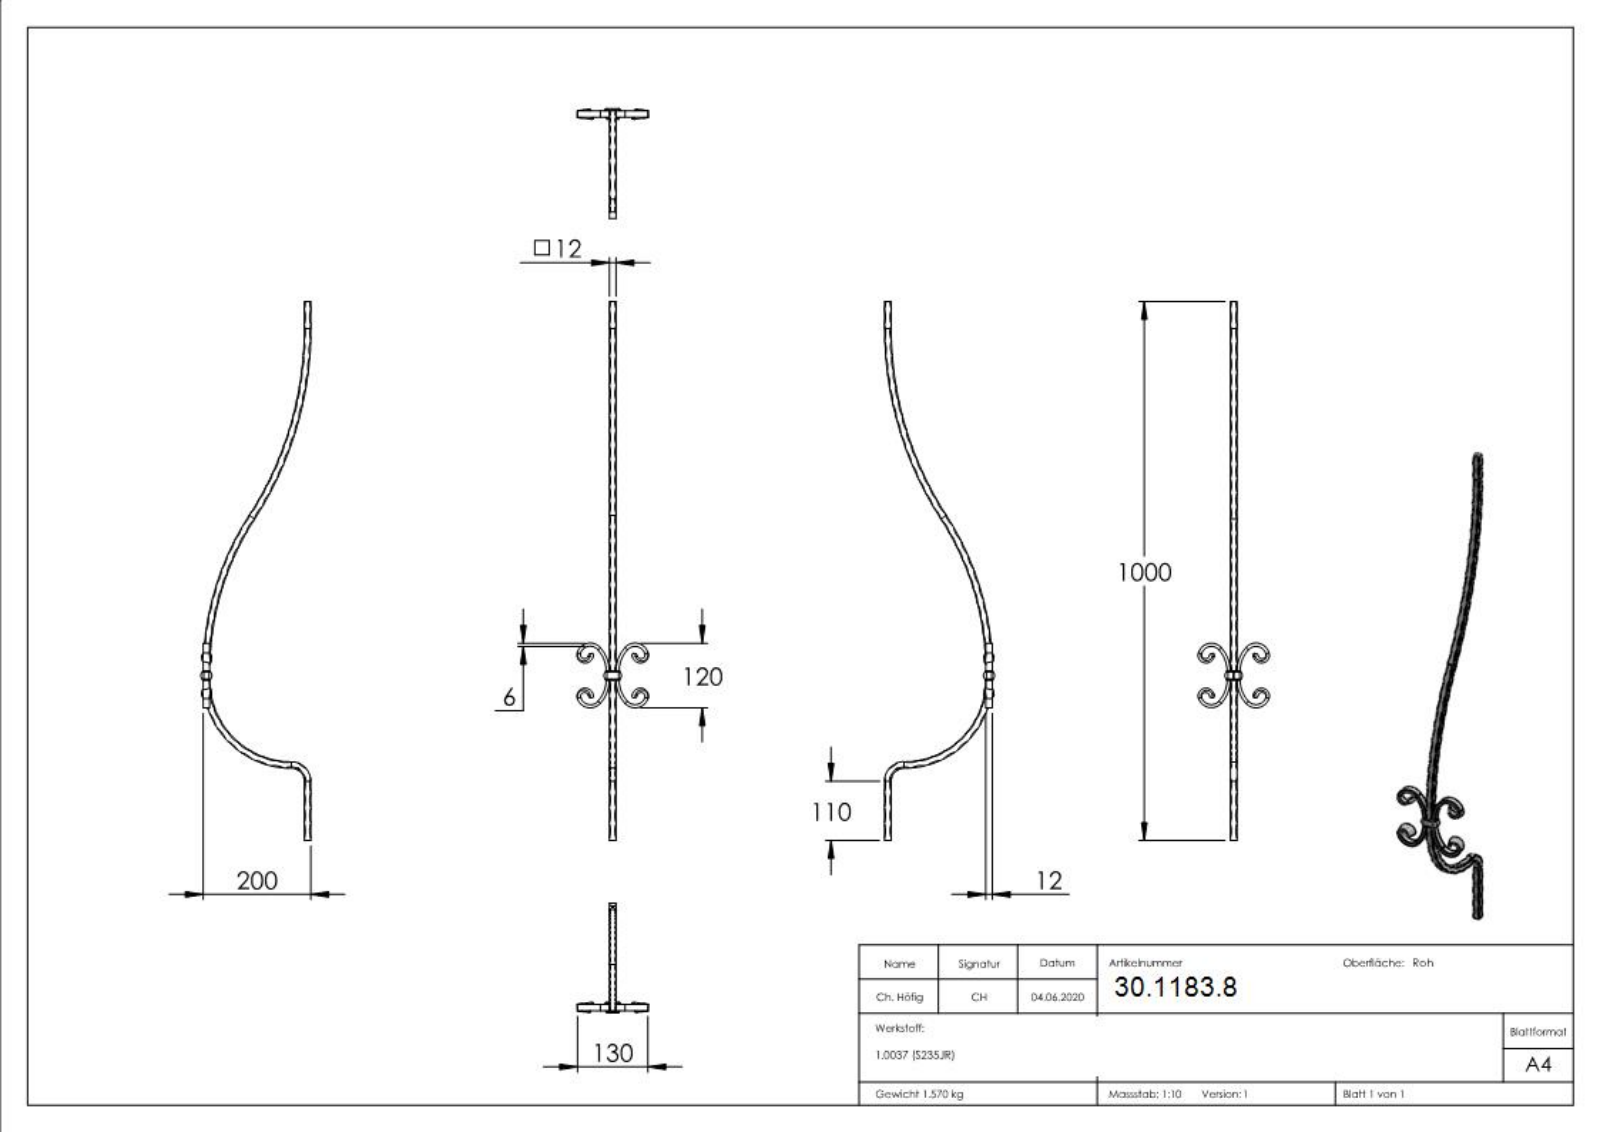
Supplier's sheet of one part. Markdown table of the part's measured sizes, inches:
| quantity | value |
| --- | --- |
| part name | 1712; 1712 Teil2; 1712 Teil2_1712 Teil2; 1712 Teil1 (+2 more) |
| STEP written by | SolidWorks 2015 (CONFIG_CONTROL_DESIGN) |
| units | inches |
| bodies | 4 solids, 453 faces (156 planar, 43 cylindrical, 254 other) |
| overall size | 39.37 × 8.031 × 5.221 |
| volume | 12.31 in³ |
| surface area | 119.9 in² |
| partial cylindrical surfaces (radius × count) | 0.031 × 8, 0.039 × 4, 0.33 × 4, 0.748 × 4, 0.984 × 4, 2.319 × 4, 2.555 × 4, 0.945 × 1 |
| main face-to-face distances | 0.472, 7.402, 7.874, 6.929, 0.236, 0.709, 0.945, 39.37, 0.453, 0.492 |
